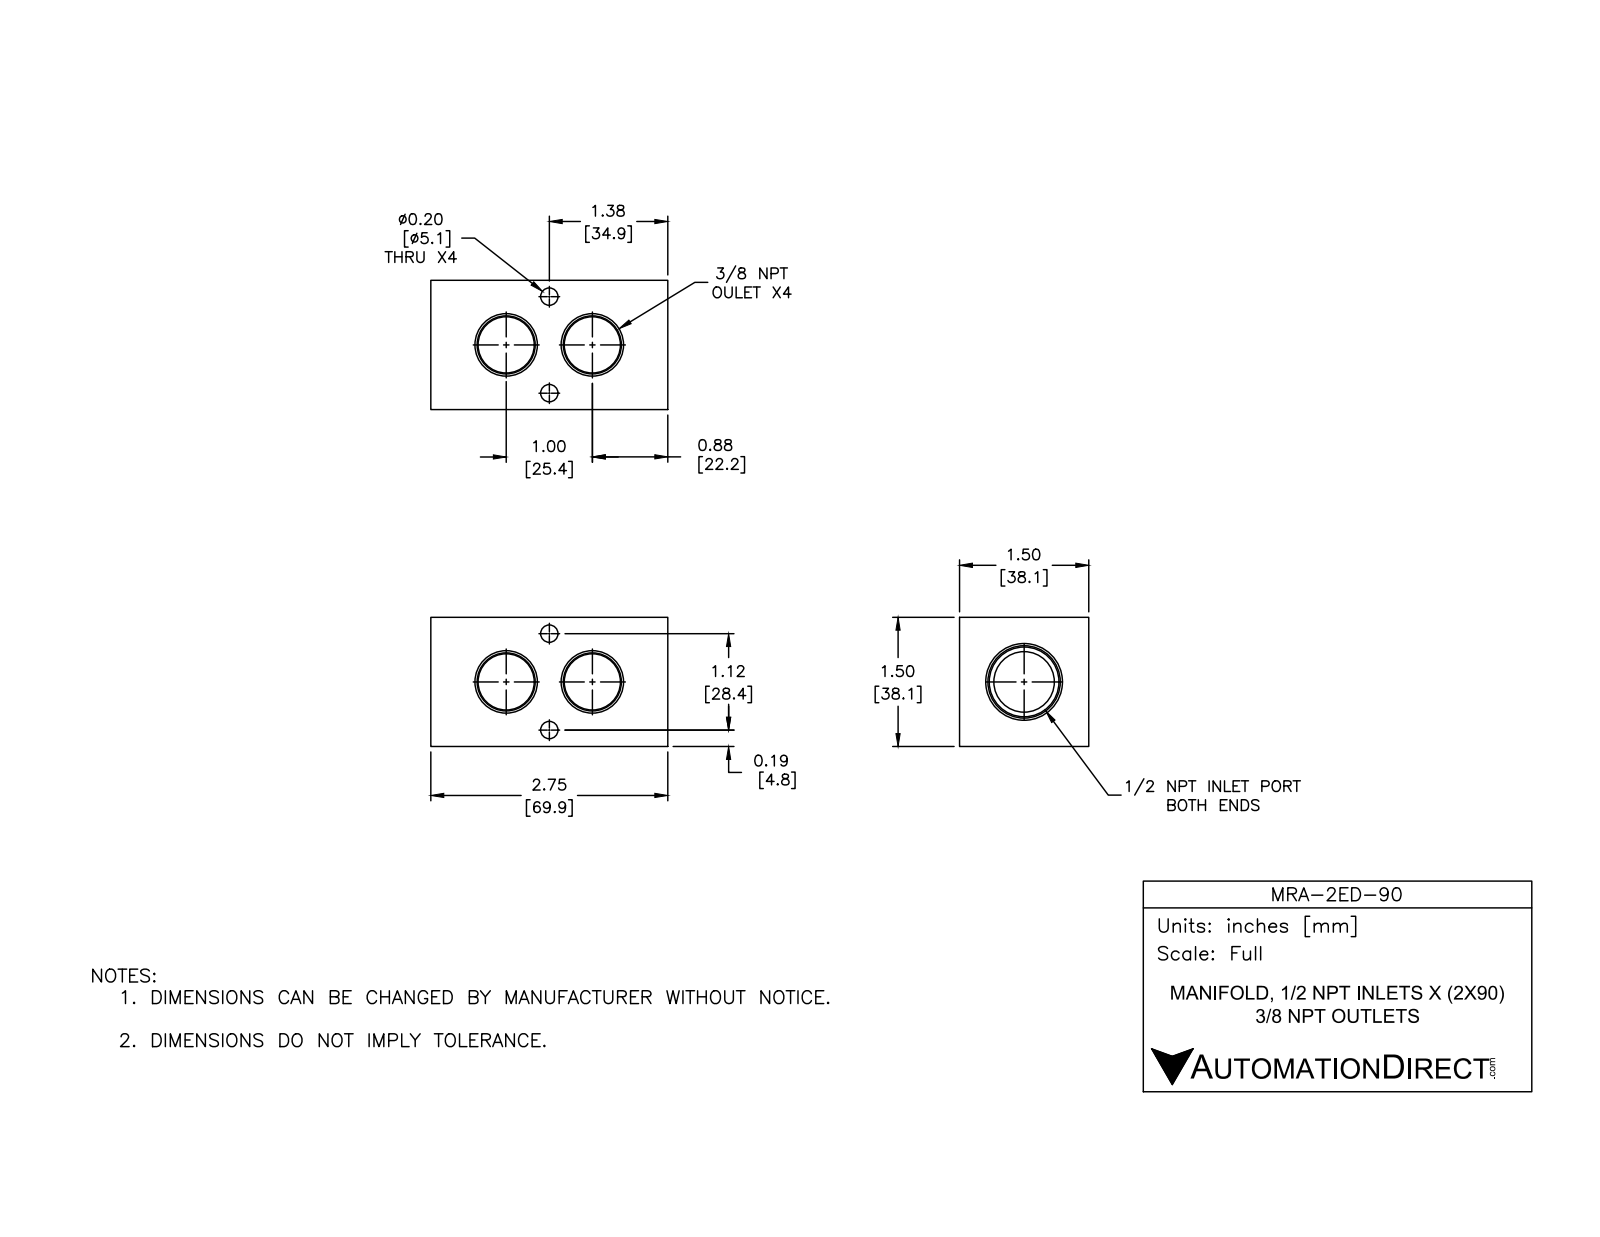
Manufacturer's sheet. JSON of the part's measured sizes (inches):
{"part_name": "MRA-2ED-90", "step_written_by": "SolidWorks 2015 (CONFIG_CONTROL_DESIGN)", "units": "inches", "bodies": {"solids": 1, "faces": 74, "planar": 16, "cylindrical": 34, "other": 24}, "overall_size": [2.75, 1.5, 1.5], "volume_in3": 4.206, "surface_area_in2": 30.78, "round_holes": [[0.2, 4], [0.562, 4], [0.703, 1]], "face_to_face_distances": [1.5, 2.75, 1.09, 0.41, 0.53, 2.22, 1.69], "hole_center_spacings": [0.751, 1, 1.12]}
